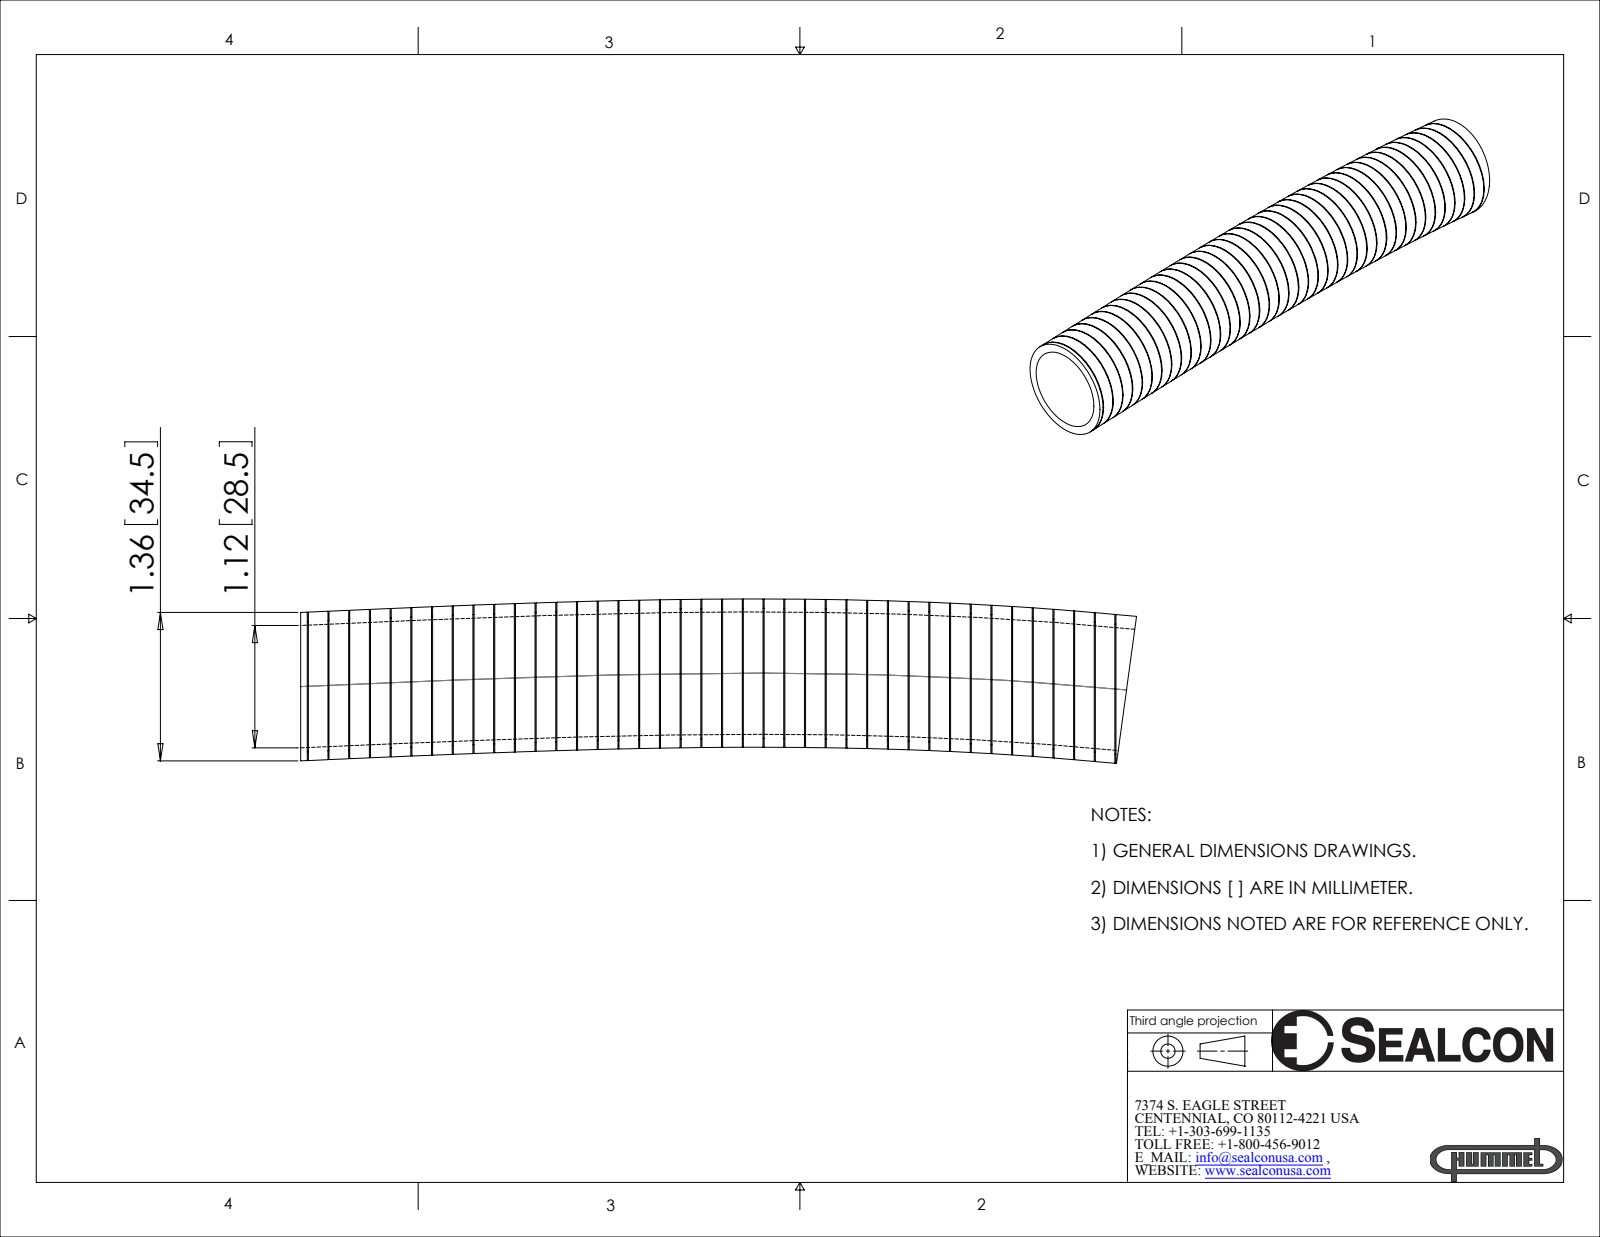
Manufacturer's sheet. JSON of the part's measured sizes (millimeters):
{"part_name": "SM-1013-HY", "step_written_by": "SolidWorks 2007 (AUTOMOTIVE_DESIGN)", "units": "millimeters", "bodies": {"solids": 1, "faces": 246, "planar": 82, "cylindrical": 80, "other": 84}, "overall_size": [194.6, 38.3, 34.5], "volume_mm3": 55770, "surface_area_mm2": 56100, "round_bosses_or_shafts": [[30.2, 39]], "face_to_face_distances": [4.8, 4.8, 9.6, 5.1, 9.6, 4.6, 5.1, 4.8, 4.5, 9.4]}
